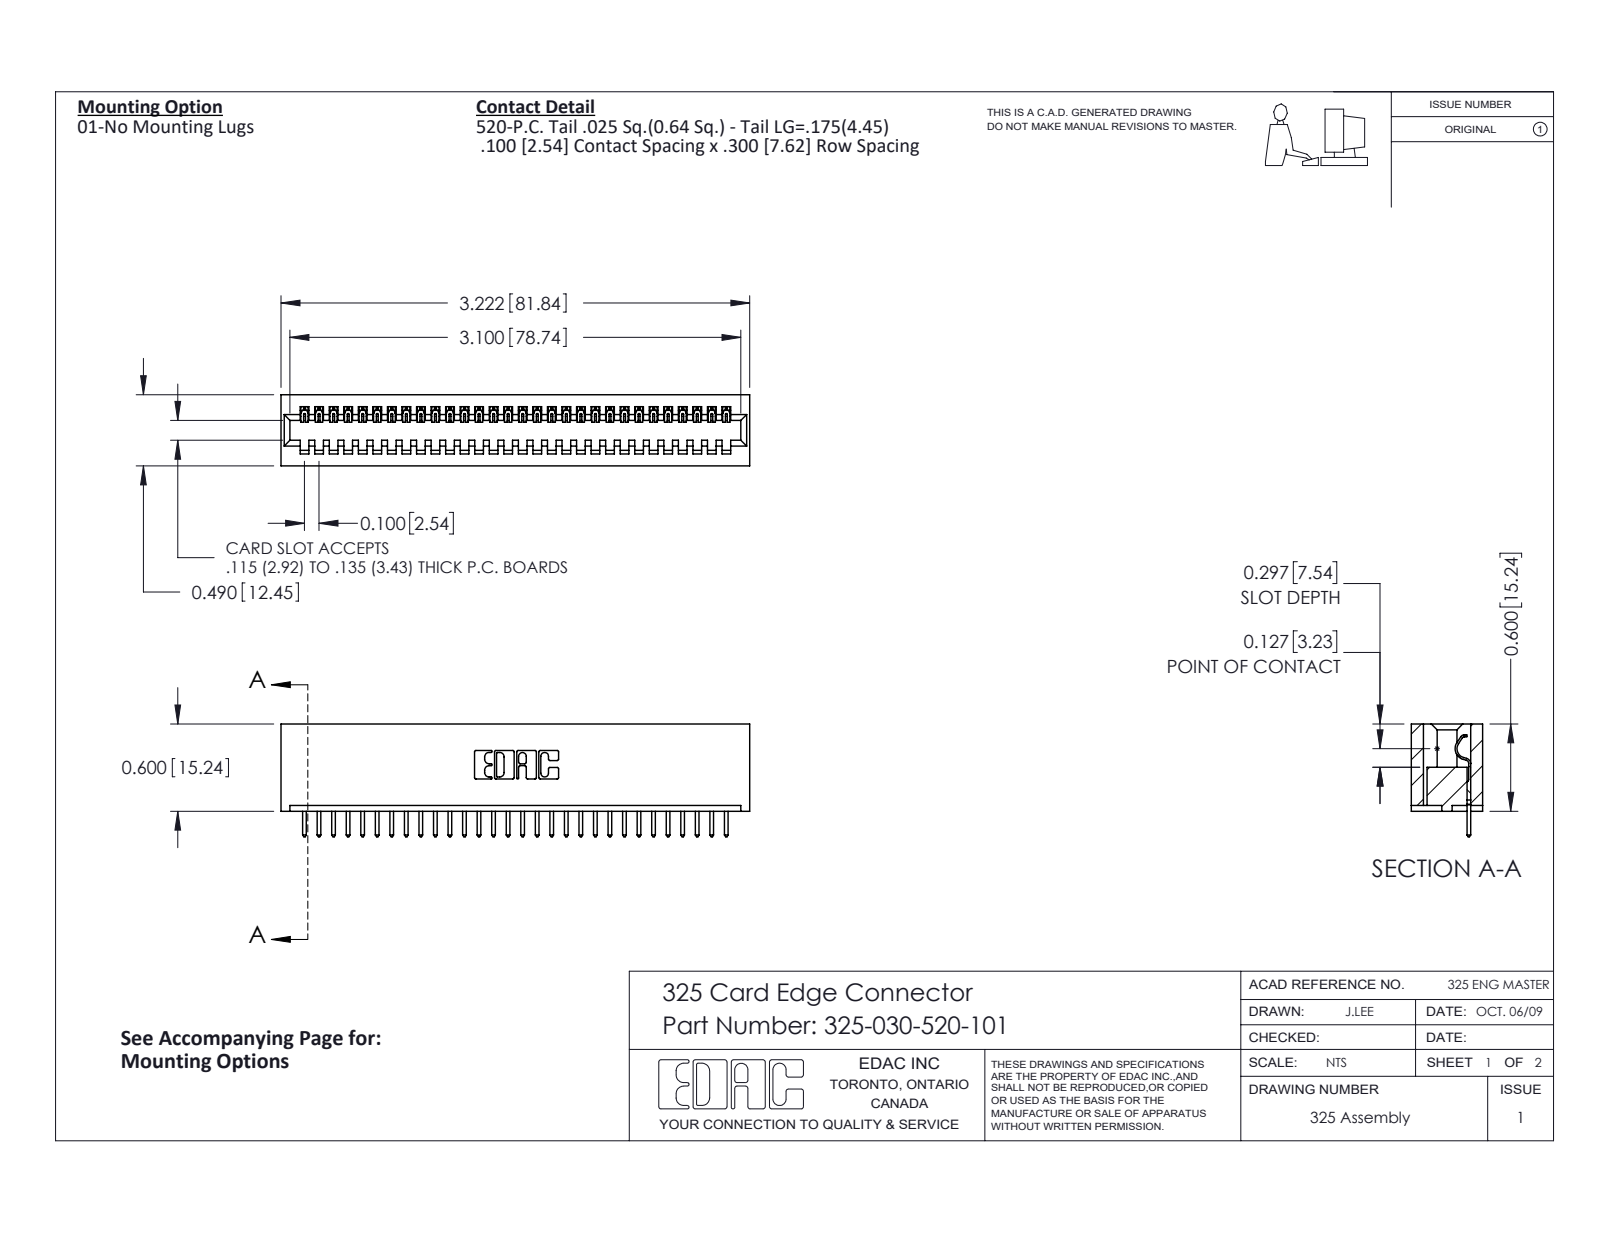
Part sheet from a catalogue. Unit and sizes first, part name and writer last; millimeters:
Units: millimetres
Overall size (bounding box): 81.8 × 19.7 × 12.4
Partial cylindrical surfaces — rounded edges, fillets, slot ends (radius × count): R0.2 ×60, R0.3 ×60, R0.3 ×22, R0.2 ×6, R0.8 ×6, R0.7 ×3, R0.4 ×1, R0.6 ×1
Main face-to-face distances: 2.1, 10.3, 12.4, 7.6, 2.7, 9.7, 0.6, 8.3, 2.5, 14.2
Volume: 10 800 mm³ · Surface area: 11 760 mm²
Bodies: 31 solids, 1846 faces (1326 planar, 520 cylindrical, 0 other)
Part name (STEP PRODUCT): 325 Part_Lugless; 325-030-520-101; 325-292-001_325-293-120
STEP written by: SolidWorks 2016 (CONFIG_CONTROL_DESIGN)
